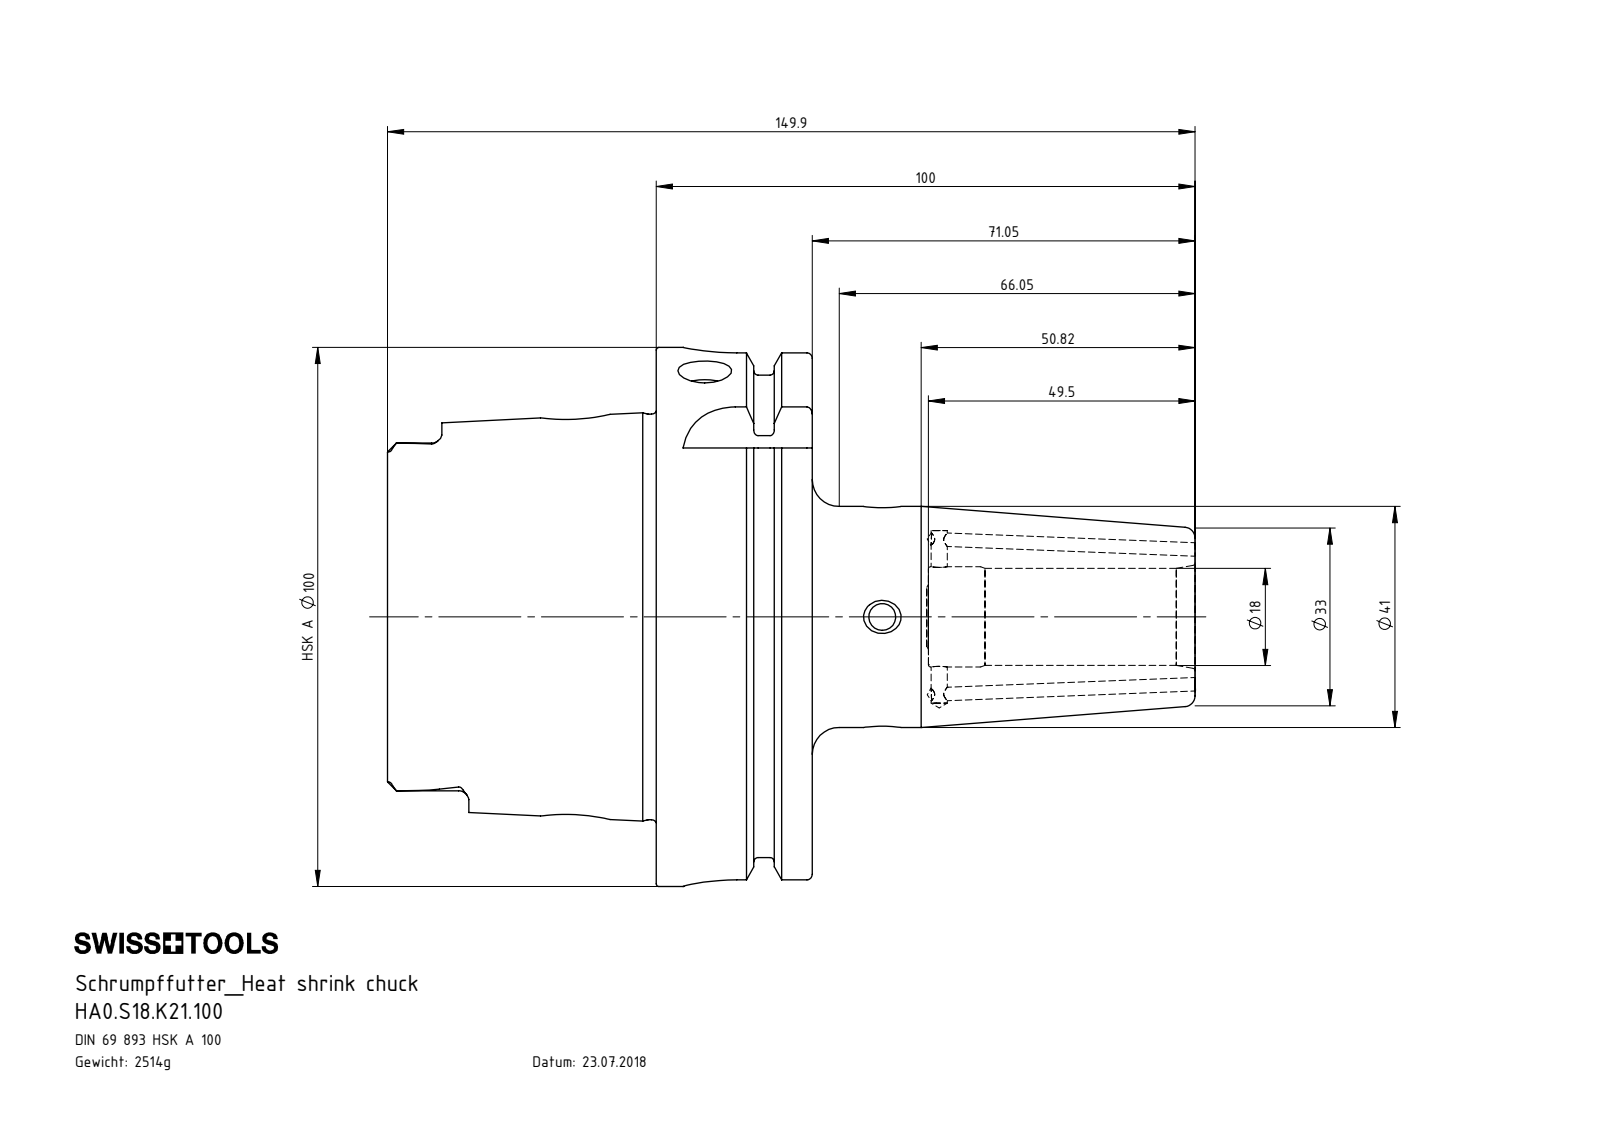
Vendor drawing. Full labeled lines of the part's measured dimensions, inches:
Part name (STEP PRODUCT): HA0-S18.K21.100_C_Fertigbearbeitung; ERU-AN5.K01.020_A; ERU-CJ2.001.006; HA0.S18.K21.100
STEP written by: SolidWorks 2017 (CONFIG_CONTROL_DESIGN)
Units: inches
Bodies: 4 solids, 295 faces (95 planar, 84 cylindrical, 116 other)
Overall size (bounding box): 5.905 × 3.937 × 3.937
Volume: 19.54 in³ · Surface area: 99.16 in²
Round holes (diameter × count): ⌀0.394 ×3, ⌀0.098 ×2, ⌀0.197 ×2, ⌀0.118 ×1, ⌀0.236 ×1, ⌀0.433 ×1, ⌀0.472 ×1, ⌀0.709 ×1, ⌀0.732 ×1, ⌀0.886 ×1, ⌀1.024 ×1, ⌀2.087 ×1
Round bosses / shafts (diameter × count): ⌀0.118 ×2, ⌀3.937 ×1, ⌀3.62 ×1, ⌀2.963 ×1, ⌀1.614 ×1, ⌀0.472 ×1
Partial cylindrical surfaces — rounded edges, fillets, slot ends (radius × count): R0.075 ×6, R0.192 ×4, R0.394 ×4
Main face-to-face distances: 1.14, 0.49, 0.65, 1.965, 2.455, 3.104, 3.457, 3.079, 1.114, 0.624
Hole centre spacings: 0.415, 1.376, 2.242, 2.657
